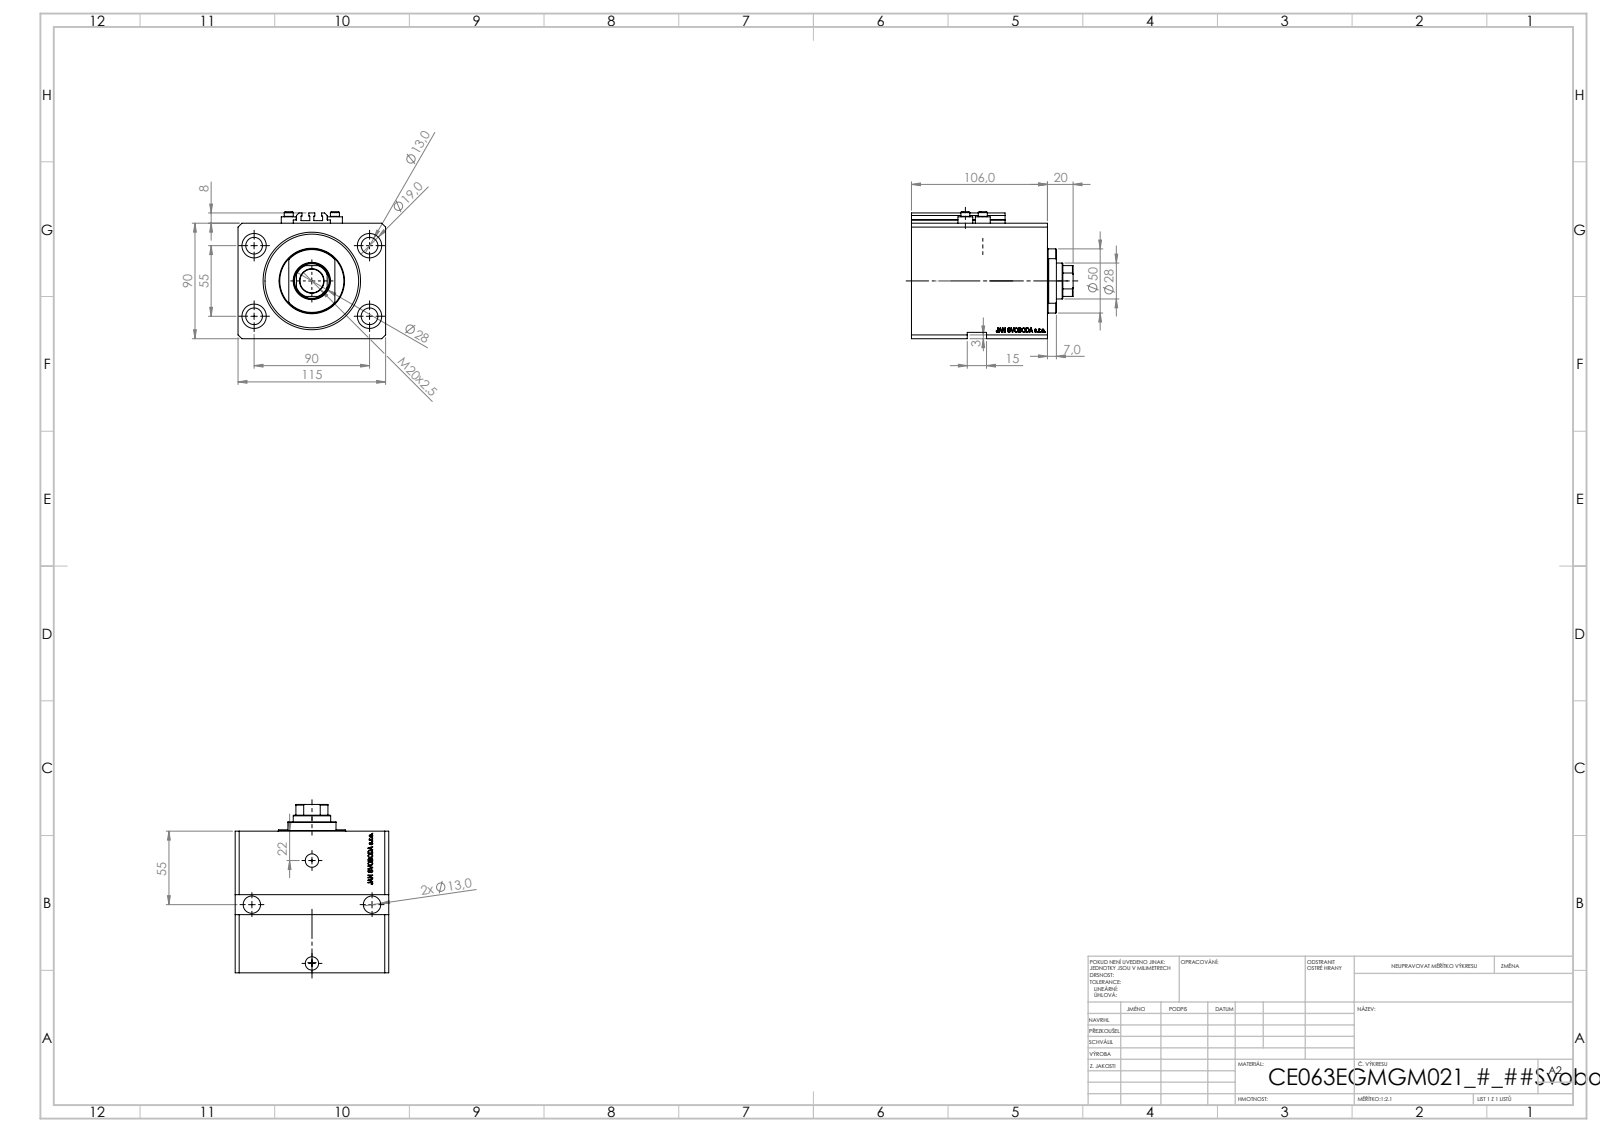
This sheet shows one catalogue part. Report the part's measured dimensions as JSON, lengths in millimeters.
{"part_name": "ALLEN BOLT V250CE; V250CE_C_VCP; V250CE_VC_E; V250CE_E_Body", "step_written_by": "SolidWorks 2019 (CONFIG_CONTROL_DESIGN)", "units": "millimeters", "bodies": {"solids": 8, "faces": 1107, "planar": 543, "cylindrical": 126, "other": 438}, "overall_size": [126, 115, 99], "volume_mm3": 961994, "surface_area_mm2": 154902, "round_holes": [[13, 6], [1.25, 4], [4, 4], [19, 4], [10, 2], [13.16, 2], [20, 2], [18.5, 1], [28, 1], [63, 1], [76, 1]], "round_bosses_or_shafts": [[11.6, 4], [7, 4], [50, 1]], "partial_cylinders_radius": [[0.2, 10], [13.5, 1]], "face_to_face_distances": [90, 115, 106, 88.1, 20, 17.9, 86, 68.1, 21, 65], "hole_center_spacings": [52.74, 90, 13.6, 27.39, 28.46, 33.62, 36, 38.48]}
